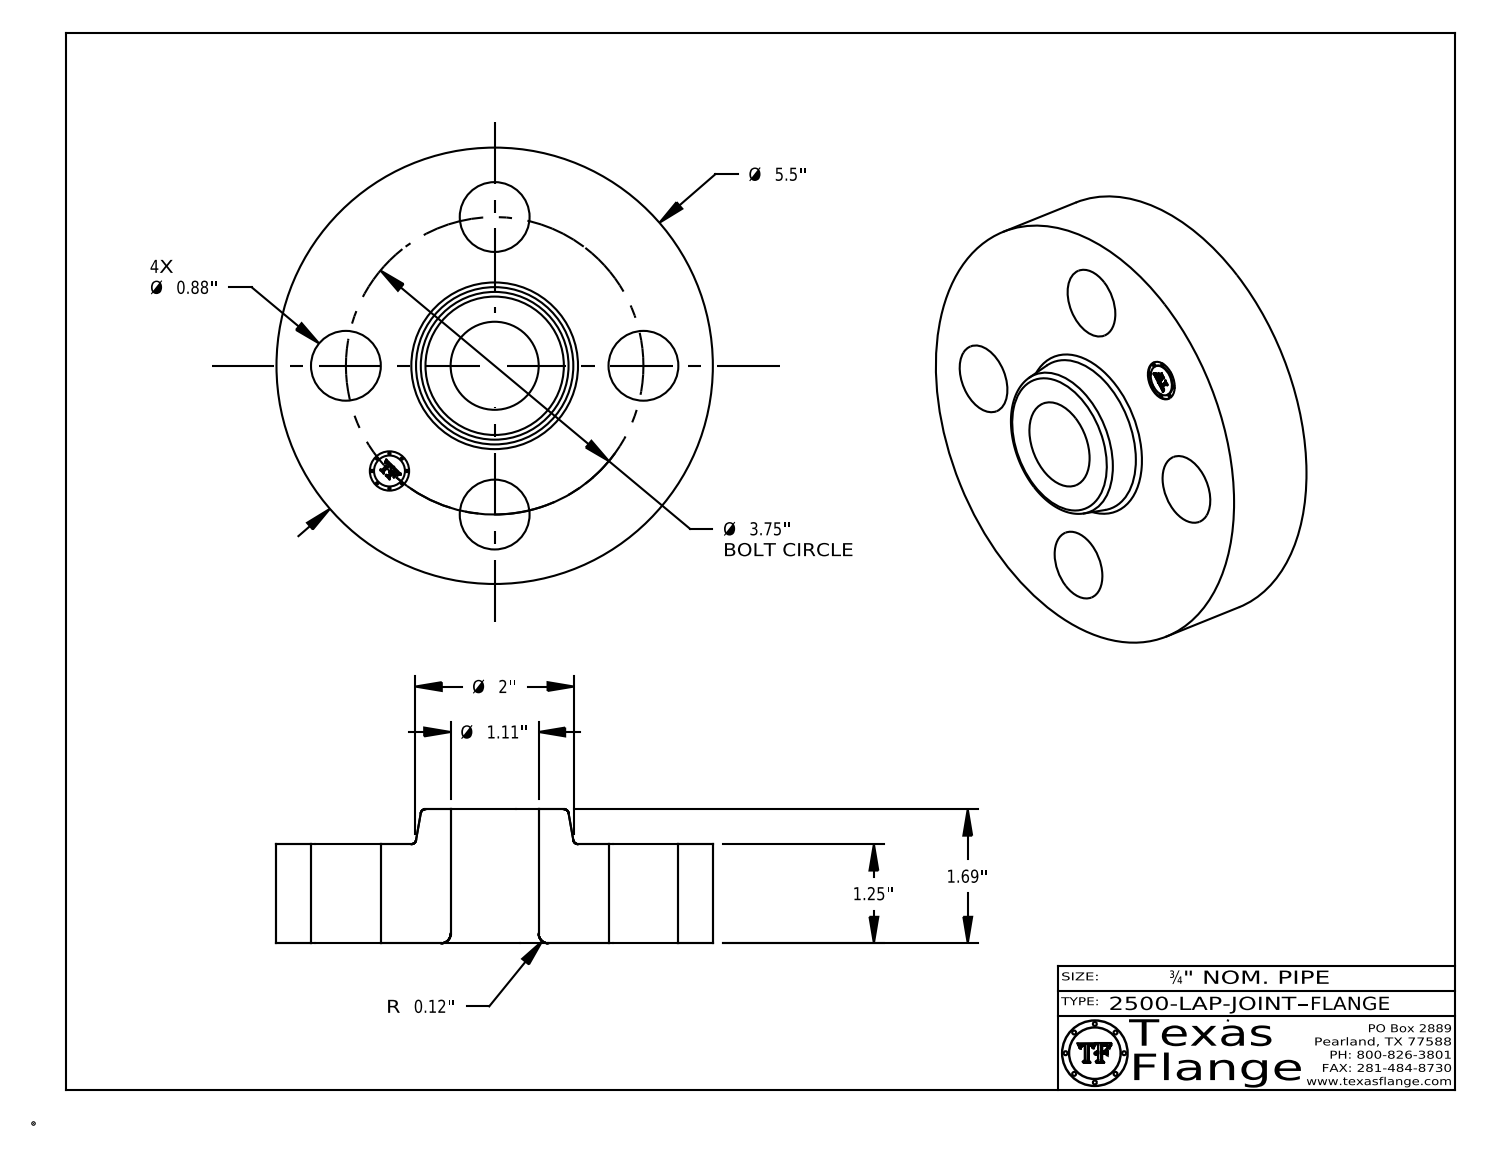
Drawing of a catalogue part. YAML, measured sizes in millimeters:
part_name: "2500-LAP-JOINT FLANGE"
step_written_by: "CATIA V5 STEP AP214 (AUTOMOTIVE_DESIGN)"
units: millimeters
bodies: {solids: 1, faces: 408, planar: 368, cylindrical: 32, other: 8}
overall_size: [139.7, 139.7, 42.9]
volume: 430800
surface_area: 54180
round_holes:
  - {diameter: 22.4, count: 4}
  - {diameter: 12.6, count: 1}
  - {diameter: 28.2, count: 1}
round_bosses_or_shafts:
  - {diameter: 0.8, count: 8}
  - {diameter: 139.7, count: 1}
  - {diameter: 9.9, count: 1}
face_to_face_distances: [31.8, 42.9, 11.2, 31.4, 0.4, 11.6, 3.8, 3.7, 0.7, 2.4]
hole_center_spacings: [47.6, 67.4, 36.4, 88, 95.3]
